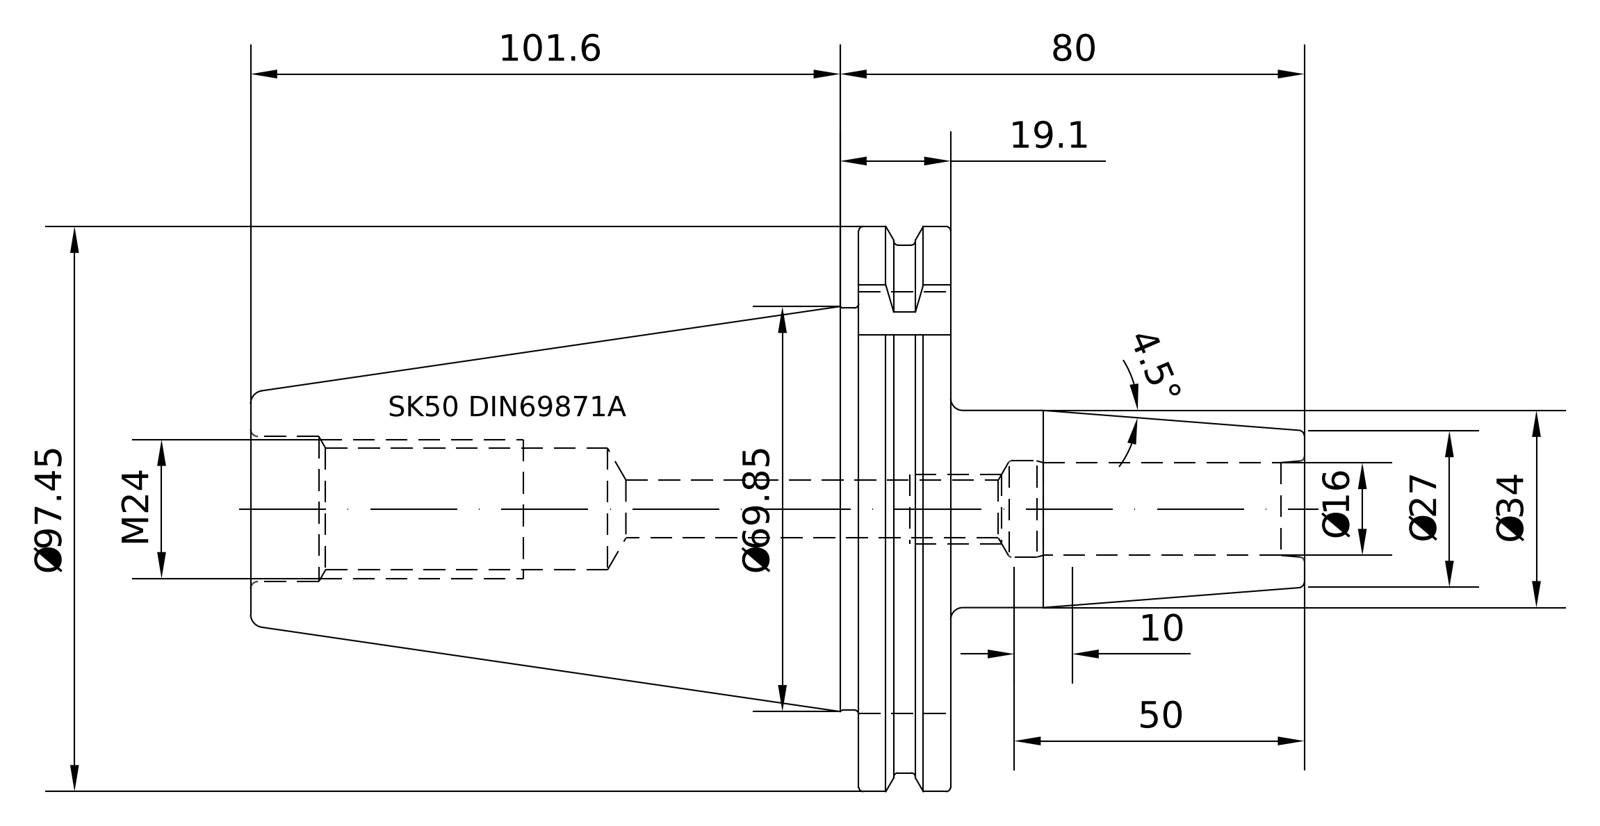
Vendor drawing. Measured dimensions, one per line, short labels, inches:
name: 50-440-16
written by: PRO/ENGINEER BY PARAMETRIC TECHNOLOGY CORPORATION, 2010430 (CONFIG_CONTROL_DESIGN)
unit: in
bodies: 1 solid, 93 faces (21 planar, 24 cylindrical, 48 other)
size: 7.15 × 3.837 × 3.701
volume: 23 in³; area: 78.64 in²
holes: 1× ⌀0.63, 1× ⌀0.817, 1× ⌀0.985, 1× ⌀1.012
bosses: 1× ⌀3.583, 1× ⌀2.722, 1× ⌀1.339, 1× ⌀0.945
rounds: 1× R0.069, 1× R1.919
face distances: 0.624, 2.866, 4.126, 4.75, 1.016, 7.15, 3.024, 2.4, 5.181, 1.055
